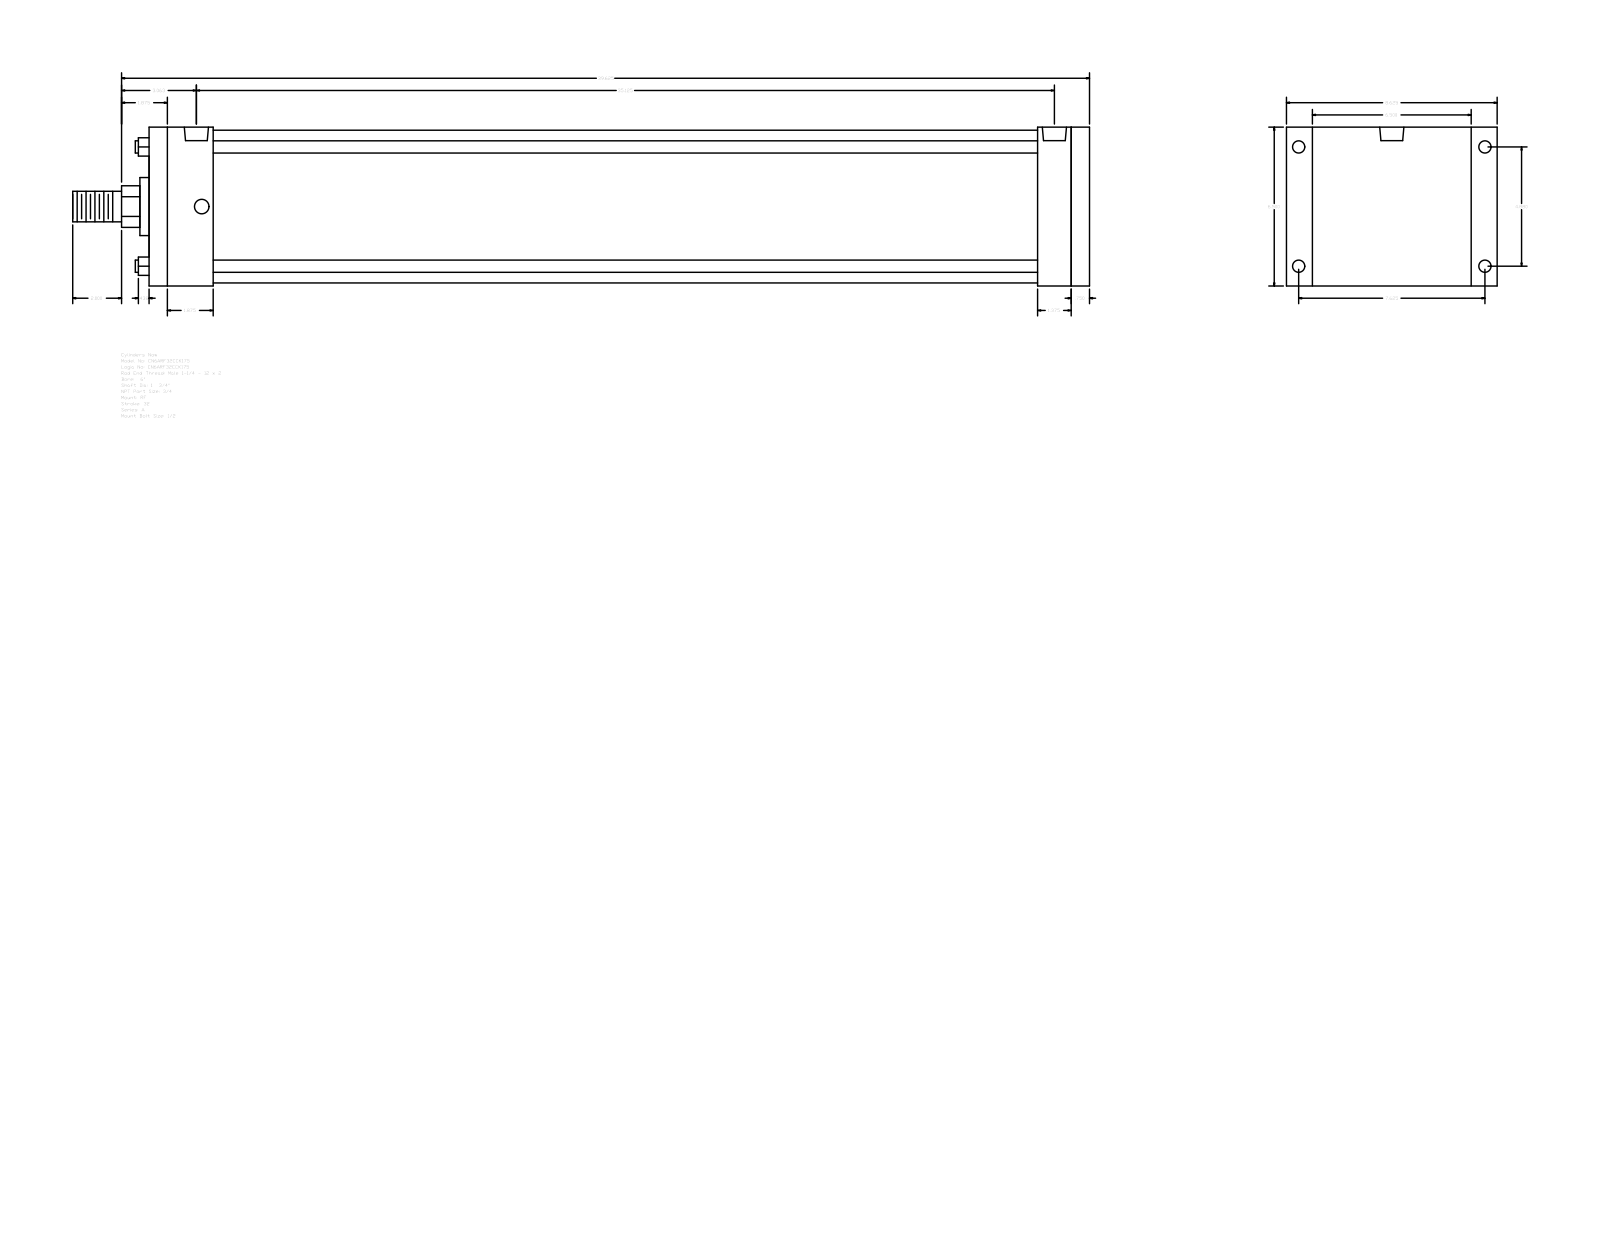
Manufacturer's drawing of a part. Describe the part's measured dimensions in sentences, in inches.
The part is named "A_RF__0600_1.75". Its 3-D file was written by "GSSL Pune (CONFIG_CONTROL_DESIGN)". It is 0 solids with 92 faces: 64 planar, 28 cylindrical and 0 other. Overall it measures 41.625 by 8.625 by 6.5 inches. Round holes: 4 of diameter 0.5, 4 of diameter 0.594, 2 of diameter 0.989. Round bosses or shafts: 4 of diameter 0.5, 1 of diameter 6.25, 1 of diameter 2.375, 1 of diameter 1.75, 1 of diameter 1.25. Partial cylindrical surfaces (rounded edges, fillets, slot ends): 1 of radius 0.852. The main face-to-face distances are 6.5, 38.5, 37.75, 0.75, 2.625, 35.125, 35.875, 36.375, 33.75, 1.375. The hole center spacings are 0.219, 4.88, 7.625, 9.053, 34.687, 34.906, 35.125.
